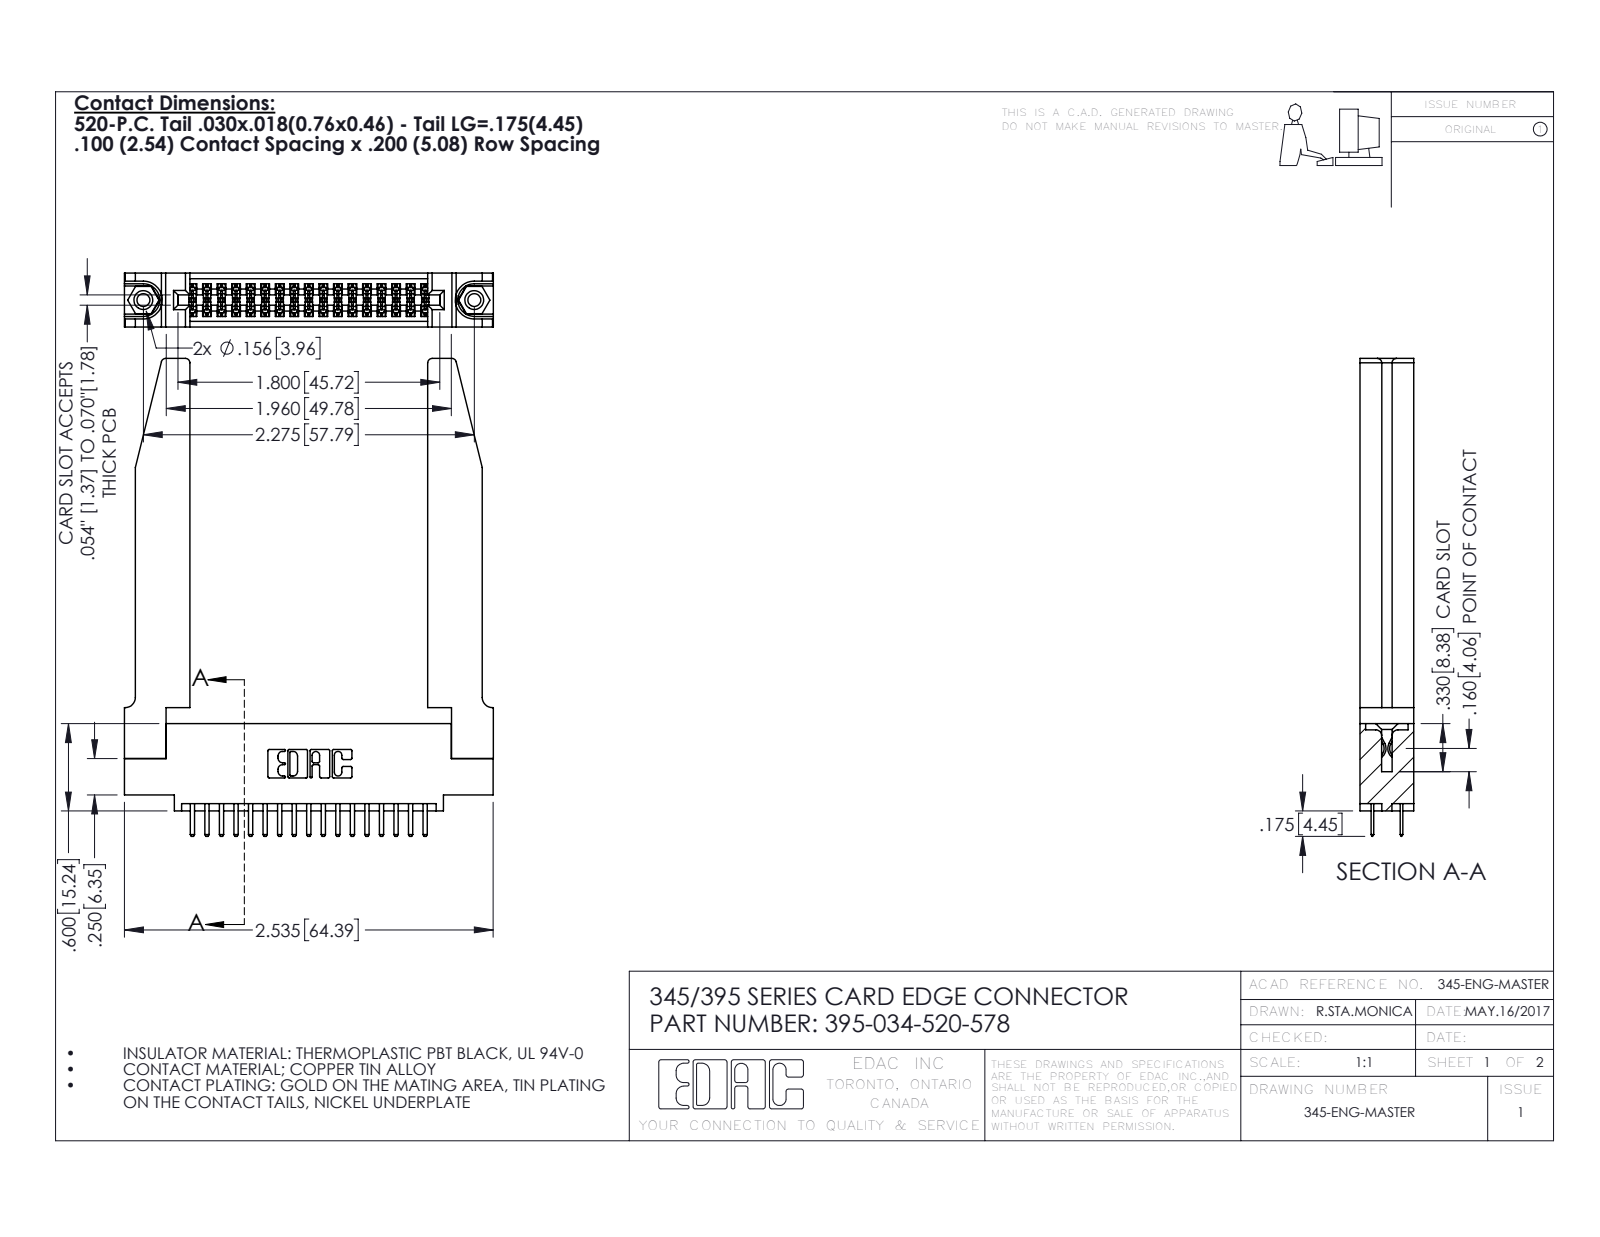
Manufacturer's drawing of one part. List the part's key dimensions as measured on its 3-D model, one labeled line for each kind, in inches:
Part name (STEP PRODUCT): 395-034-520-578; 345-250-001_345-250-001-102; 345-220-078_345-220-078; 345-292-001_345-293-120 (+1 more)
STEP written by: SolidWorks 2016 (CONFIG_CONTROL_DESIGN)
Units: inches
Bodies: 39 solids, 2200 faces (1416 planar, 732 cylindrical, 52 other)
Overall size (bounding box): 3.285 × 2.536 × 0.37
Volume: 0.836 in³ · Surface area: 23.55 in²
Round holes (diameter × count): ⌀0.089 ×2, ⌀0.125 ×2, ⌀0.156 ×2, ⌀0.064 ×1
Round bosses / shafts (diameter × count): ⌀0.155 ×2
Partial cylindrical surfaces — rounded edges, fillets, slot ends (radius × count): R0.006 ×51, R0.01 ×38, R0.01 ×22, R0.03 ×8, R0.007 ×6, R0.031 ×6, R0.026 ×3, R0.014 ×2
Main face-to-face distances: 0.37, 0.072, 0.298, 0.2, 0.098, 0.272, 0.025, 0.15, 0.22, 0.077
Hole centre spacings: 0.27, 2.041, 2.275
